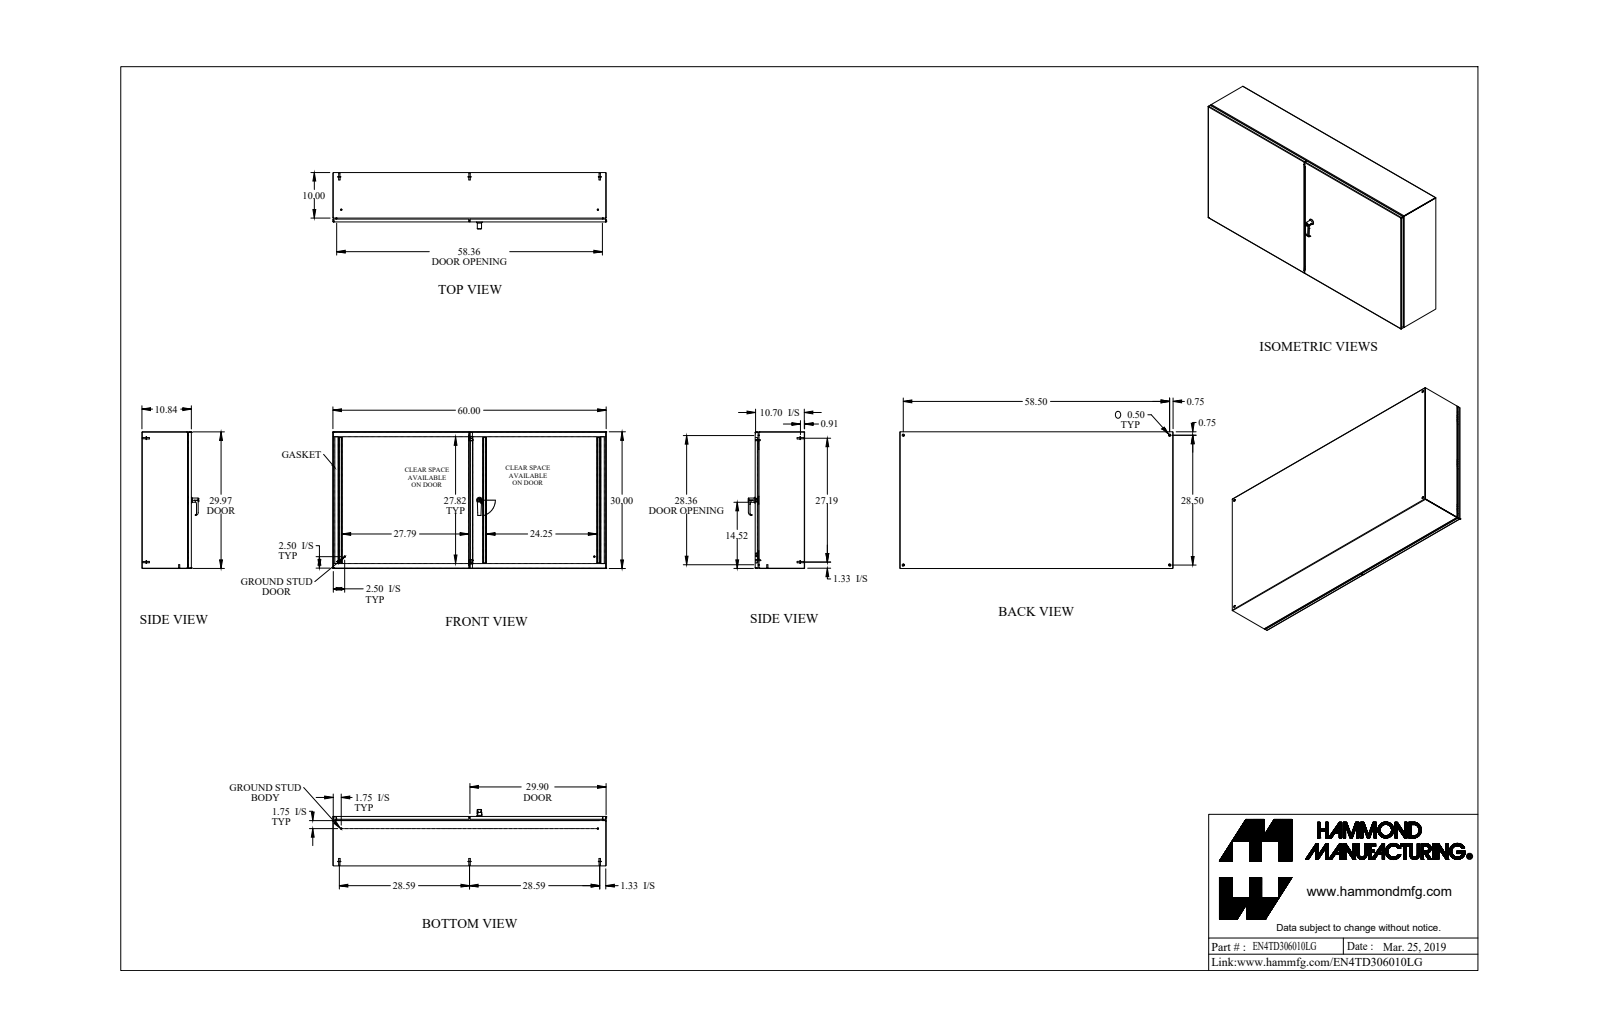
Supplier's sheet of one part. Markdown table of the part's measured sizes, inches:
| quantity | value |
| --- | --- |
| part name | EN4TD306010LG |
| STEP written by | SolidWorks 2018 (AUTOMOTIVE_DESIGN) |
| units | inches |
| bodies | 91 solids, 2297 faces (1053 planar, 846 cylindrical, 398 other) |
| overall size | 60 × 30 × 12.372 |
| volume | 484.3 in³ |
| surface area | 12 929 in² |
| round holes (diameter × count) | 0.196 × 5, 0.176 × 4, 0.265 × 4, 0.5 × 4, 0.24 × 3, 0.242 × 3, 0.172 × 2, 0.25 × 2, 0.256 × 2, 0.26 × 2, 0.275 × 2, 0.313 × 2 |
| round bosses / shafts (diameter × count) | 0.25 × 10, 0.625 × 8, 0.313 × 6, 0.27 × 6, 0.51 × 4, 0.281 × 4, 0.156 × 4, 0.75 × 3 |
| partial cylindrical surfaces (radius × count) | 0.043 × 30, 0.081 × 30, 0.036 × 26, 0.108 × 26, 0.063 × 25, 0.094 × 20, 0.02 × 16, 0.016 × 15 |
| main face-to-face distances | 0.072, 10.77, 10.698, 10.842, 29.928, 29.856, 59.928, 30, 59.856, 60 |
| hole center spacings | 0.786, 13.188, 26.792, 28.5, 30.603, 31.748, 34.498, 58.5 |
